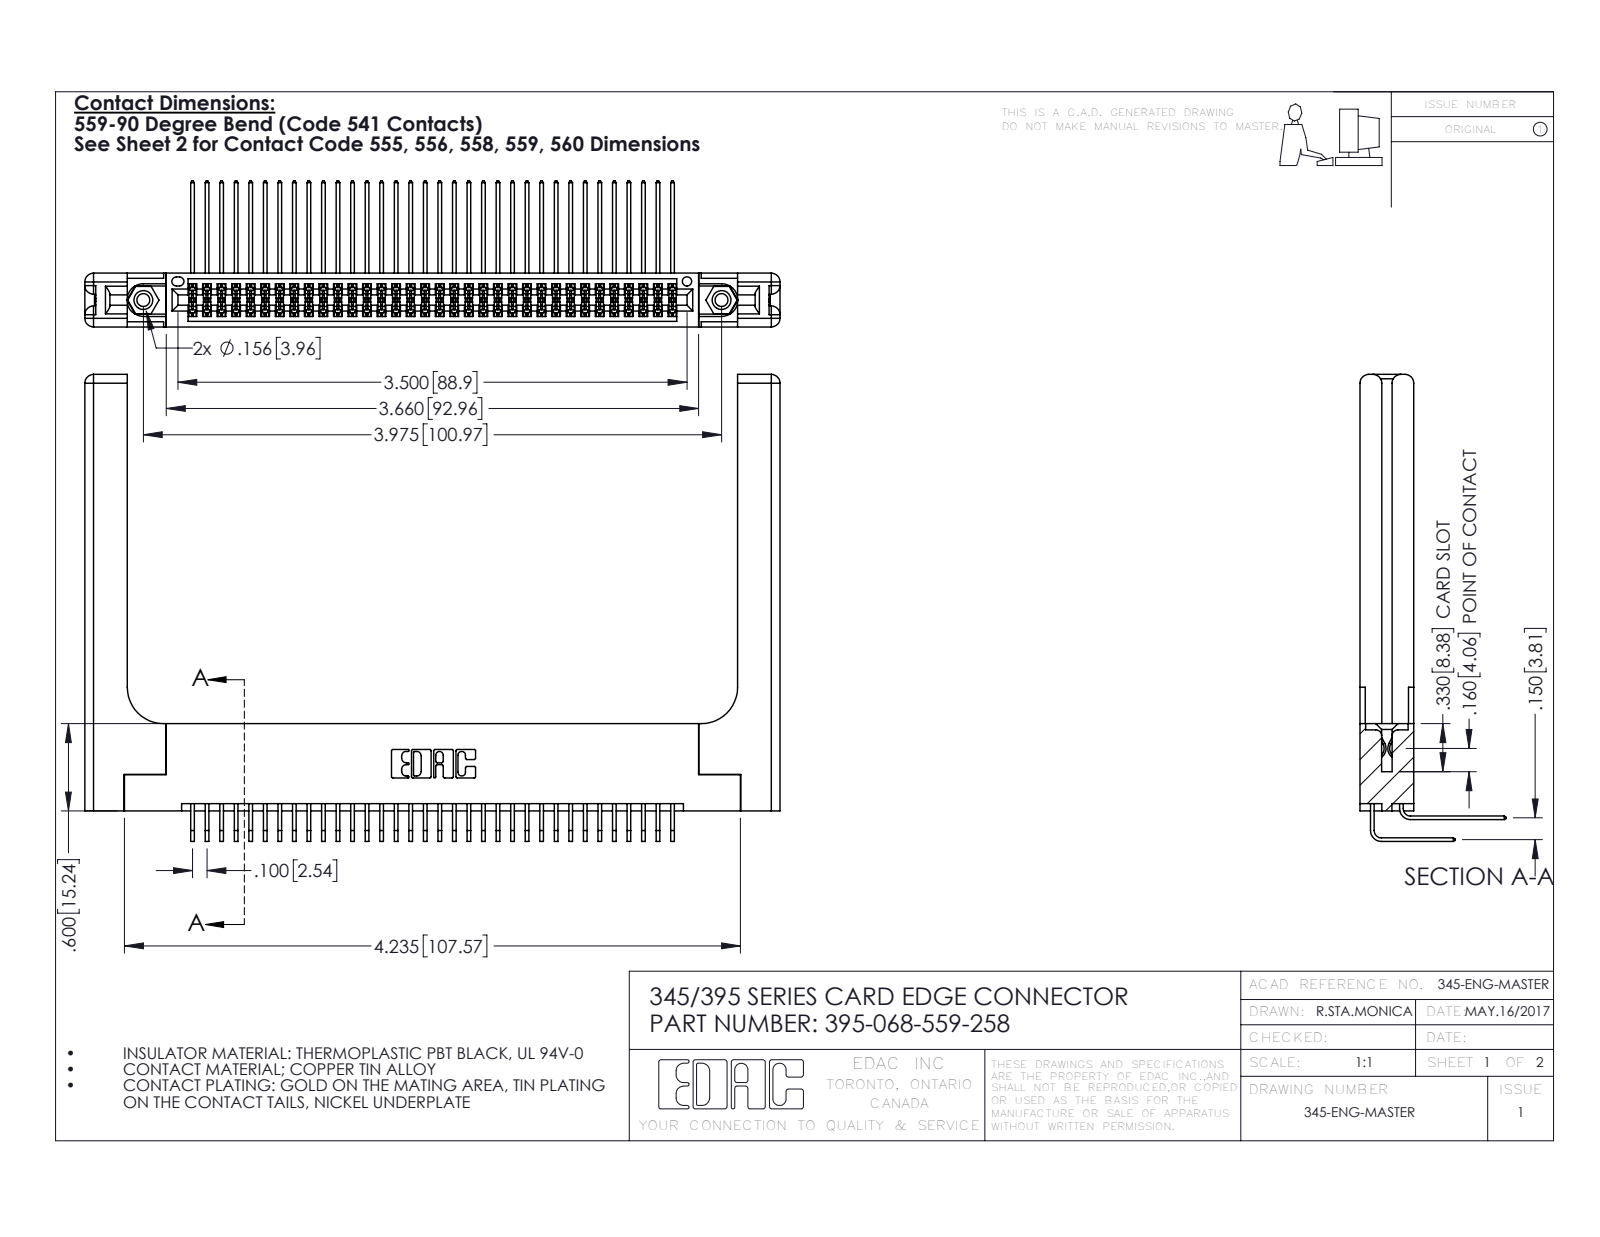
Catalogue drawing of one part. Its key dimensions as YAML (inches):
part_name: "345-292-001_558 559 Tail - 1; 395-068-559-258; 345-250-001_345-250-001-102; 345-292-001_559 Tail - 2 (+2 more)"
step_written_by: "SolidWorks 2016 (CONFIG_CONTROL_DESIGN)"
units: inches
bodies: {solids: 73, faces: 3918, planar: 2608, cylindrical: 1250, other: 60}
overall_size: [4.779, 3.209, 1.005]
volume: 1.256
surface_area: 38.21
round_holes:
  - {diameter: 0.089, count: 2}
  - {diameter: 0.125, count: 2}
  - {diameter: 0.156, count: 2}
  - {diameter: 0.064, count: 1}
round_bosses_or_shafts:
  - {diameter: 0.155, count: 2}
partial_cylinders:
  - {radius: 0.006, count: 103}
  - {radius: 0.01, count: 22}
  - {radius: 0.06, count: 16}
  - {radius: 0.007, count: 6}
  - {radius: 0.031, count: 6}
  - {radius: 0.026, count: 3}
  - {radius: 0.014, count: 2}
  - {radius: 0.019, count: 2}
face_to_face_distances: [0.072, 0.37, 0.298, 0.2, 0.098, 0.272, 0.025, 0.225, 0.148, 0.15]
hole_center_spacings: [0.27, 3.74, 3.975]
